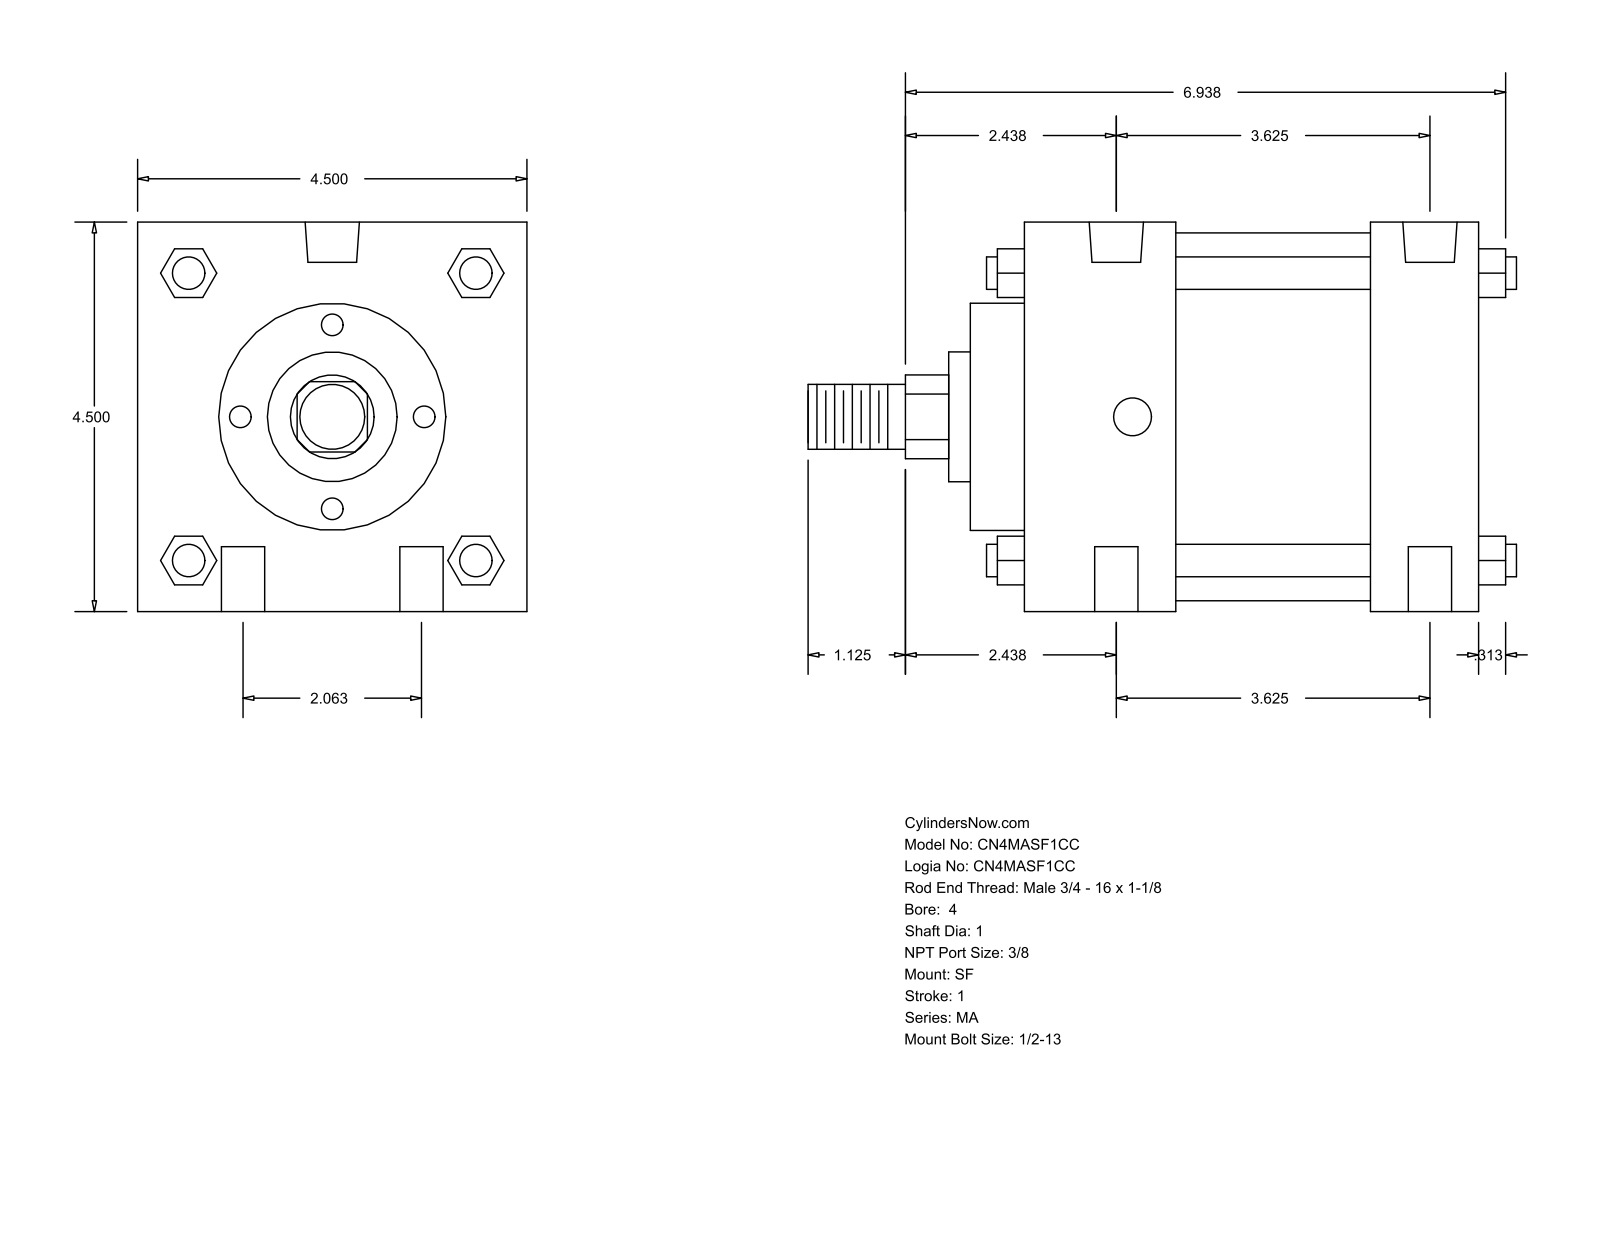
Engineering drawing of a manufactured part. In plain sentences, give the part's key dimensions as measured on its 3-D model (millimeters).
The part is named "MA_SF__0400_1". Its 3-D file was written by "GSSL Pune (CONFIG_CONTROL_DESIGN)". It is 0 solids with 126 faces: 95 planar, 31 cylindrical and 0 other. Overall it measures 207.96 by 114.3 by 114.3 millimeters. Round holes: 4 of diameter 12.7, 2 of diameter 11.11, 2 of diameter 15.93. Round bosses or shafts: 4 of diameter 9.53, 1 of diameter 107.95, 1 of diameter 66.67, 1 of diameter 38.1, 1 of diameter 25.4, 1 of diameter 19.05. Partial cylindrical surfaces (rounded edges, fillets, slot ends): 1 of radius 12.29. The main face-to-face distances are 114.3, 133.36, 101.61, 31.75, 44.46, 57.15, 88.9, 15.87, 60.33, 117.48. The hole center spacings are 26.19, 95.73, 92.08, 52.38, 105.94, 82.55.
